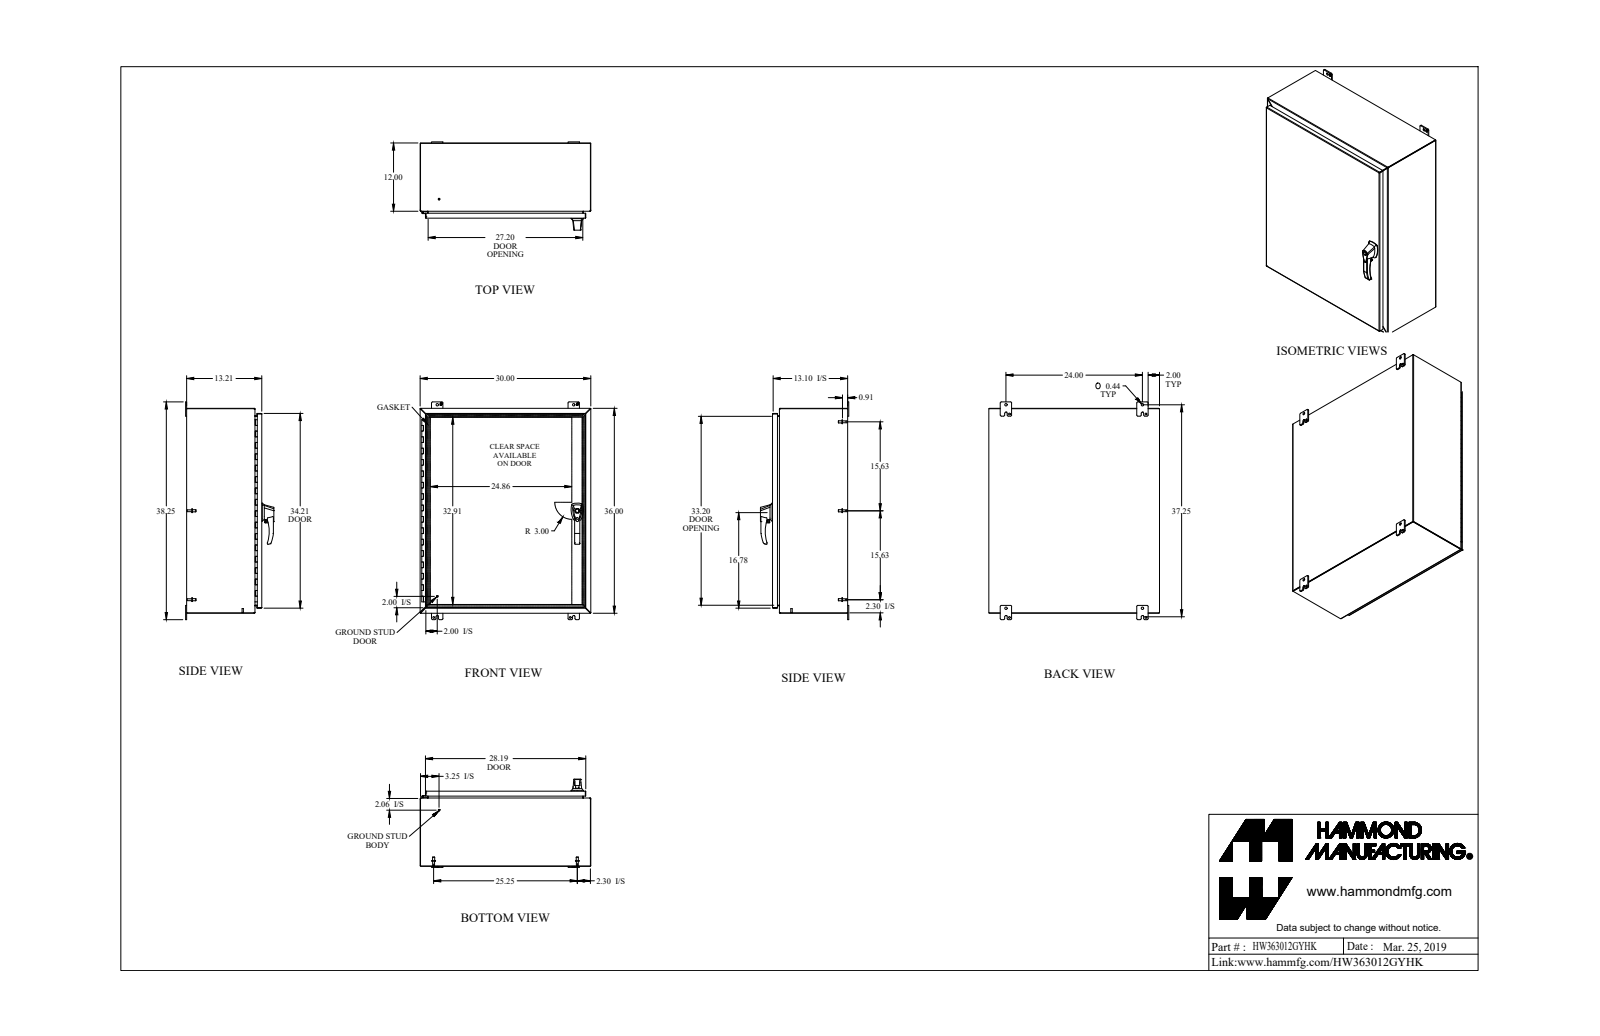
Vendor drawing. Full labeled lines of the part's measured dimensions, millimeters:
Part name (STEP PRODUCT): HW363012GYHK
STEP written by: SolidWorks 2018 (AUTOMOTIVE_DESIGN)
Units: millimetres
Bodies: 48 solids, 1609 faces (773 planar, 655 cylindrical, 181 other)
Overall size (bounding box): 971.6 × 762 × 394
Volume: 5 703 000 mm³ · Surface area: 5 948 000 mm²
Round holes (diameter × count): ⌀4.5 ×6, ⌀6.4 ×4, ⌀8 ×4, ⌀5 ×3, ⌀6.7 ×3, ⌀10.5 ×3, ⌀6.5 ×2, ⌀10 ×2, ⌀11.1 ×2, ⌀4.7 ×1, ⌀5.9 ×1, ⌀8.5 ×1
Round bosses / shafts (diameter × count): ⌀9.5 ×11, ⌀16.5 ×6, ⌀8.4 ×6, ⌀6.4 ×6, ⌀4 ×6, ⌀25.4 ×3, ⌀16 ×2, ⌀13 ×2
Partial cylindrical surfaces — rounded edges, fillets, slot ends (radius × count): R4.8 ×34, R6.4 ×31, R0.9 ×18, R2.7 ×18, R1.5 ×12, R2.9 ×12, R3.2 ×9, R1 ×8
Main face-to-face distances: 1.8, 1.8, 333.7, 331.9, 335.5, 333.7, 760.2, 912.6, 758.3, 762
Hole centre spacings: 358.6, 358.6, 717.2, 28.2, 294.1, 358.6, 609.6, 627.9
